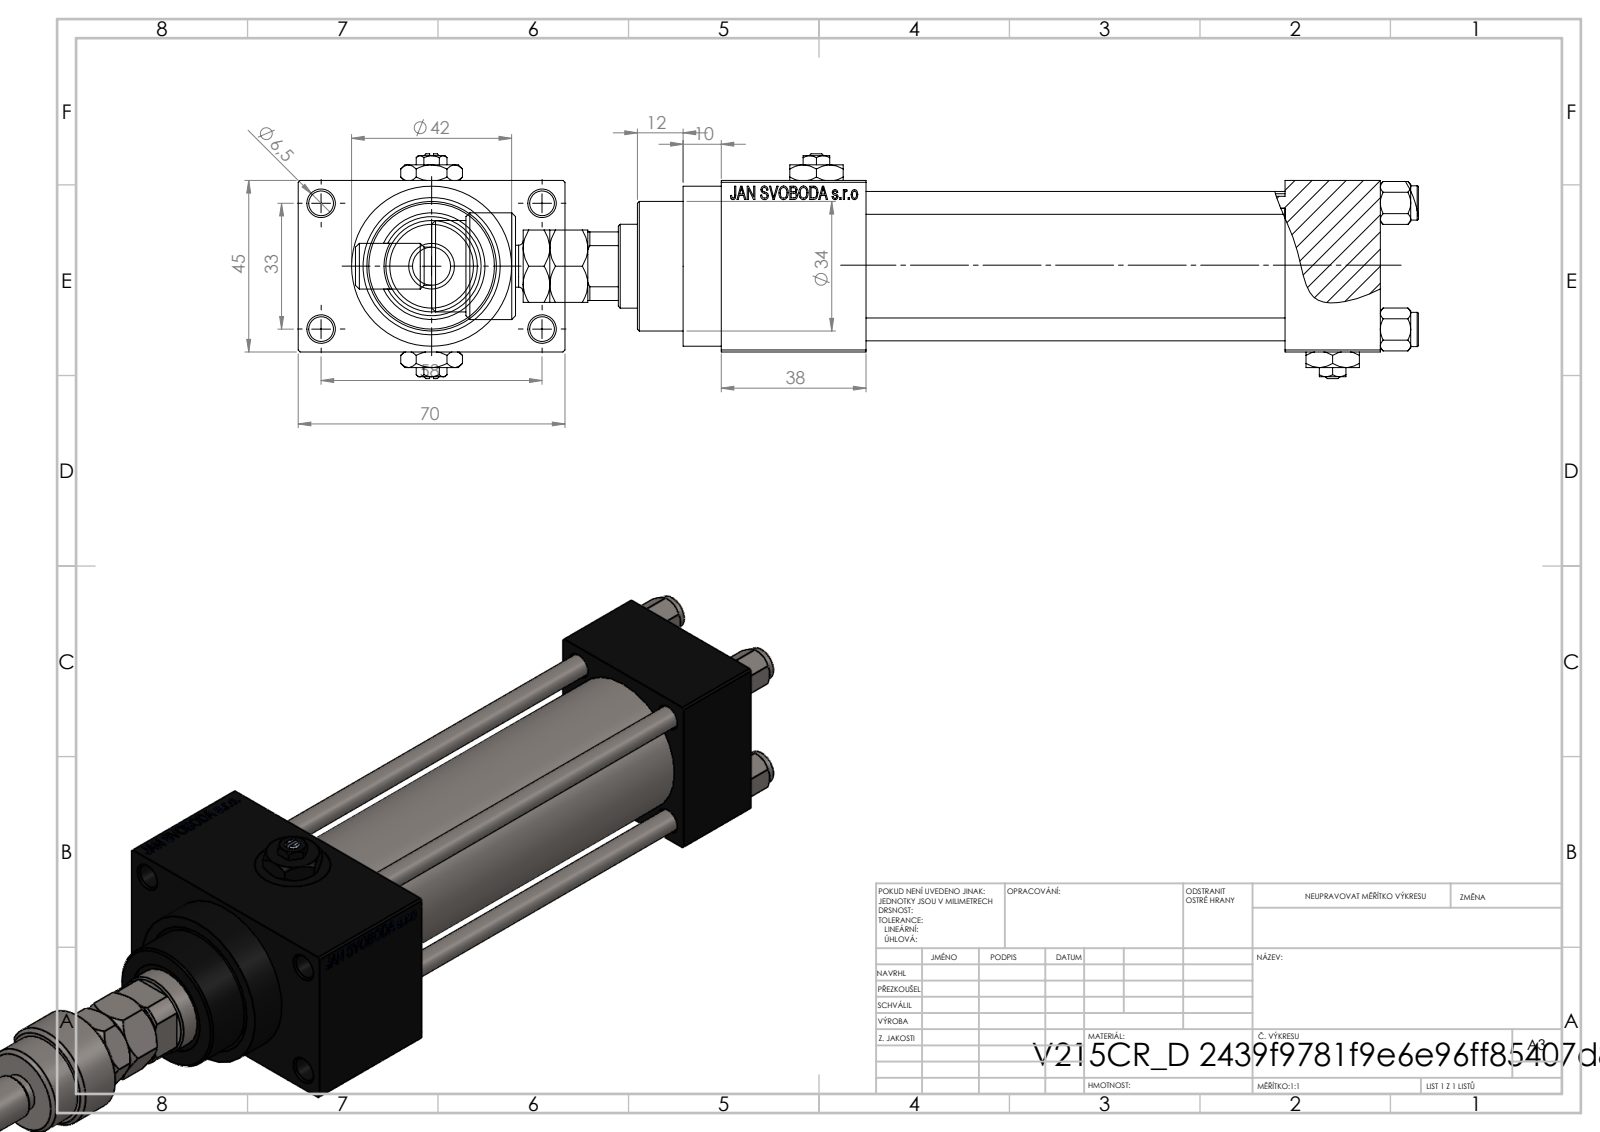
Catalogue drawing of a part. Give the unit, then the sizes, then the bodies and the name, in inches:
Units: inches
Overall size (bounding box): 10.984 × 2.756 × 2.323
Round holes (diameter × count): ⌀0.236 ×4, ⌀0.256 ×4, ⌀0.276 ×2, ⌀0.518 ×2, ⌀0.787 ×2, ⌀0.413 ×1, ⌀0.866 ×1, ⌀0.945 ×1, ⌀0.984 ×1, ⌀1.26 ×1, ⌀1.299 ×1
Round bosses / shafts (diameter × count): ⌀0.354 ×4, ⌀1.654 ×1, ⌀1.496 ×1, ⌀1.339 ×1, ⌀1.102 ×1, ⌀0.709 ×1, ⌀0.472 ×1, ⌀0.433 ×1
Partial cylindrical surfaces — rounded edges, fillets, slot ends (radius × count): R0.384 ×1, R0.413 ×1
Main face-to-face distances: 1.772, 0.984, 0.492, 2.264, 4.331, 5.315, 1.496, 5.827, 2.756, 6.811
Hole centre spacings: 0.488, 0.924, 1.307, 1.314, 1.392, 1.795, 2.219, 1.299
Volume: 19.13 in³ · Surface area: 169.8 in²
Bodies: 15 solids, 1274 faces (568 planar, 102 cylindrical, 604 other)
Part name (STEP PRODUCT): FEMALE_PART_FOR_DFA; NUT_M5_D; V215CR_VCP_D; V215CR_D_TYCINKA (+4 more)
STEP written by: SolidWorks 2019 (CONFIG_CONTROL_DESIGN)
